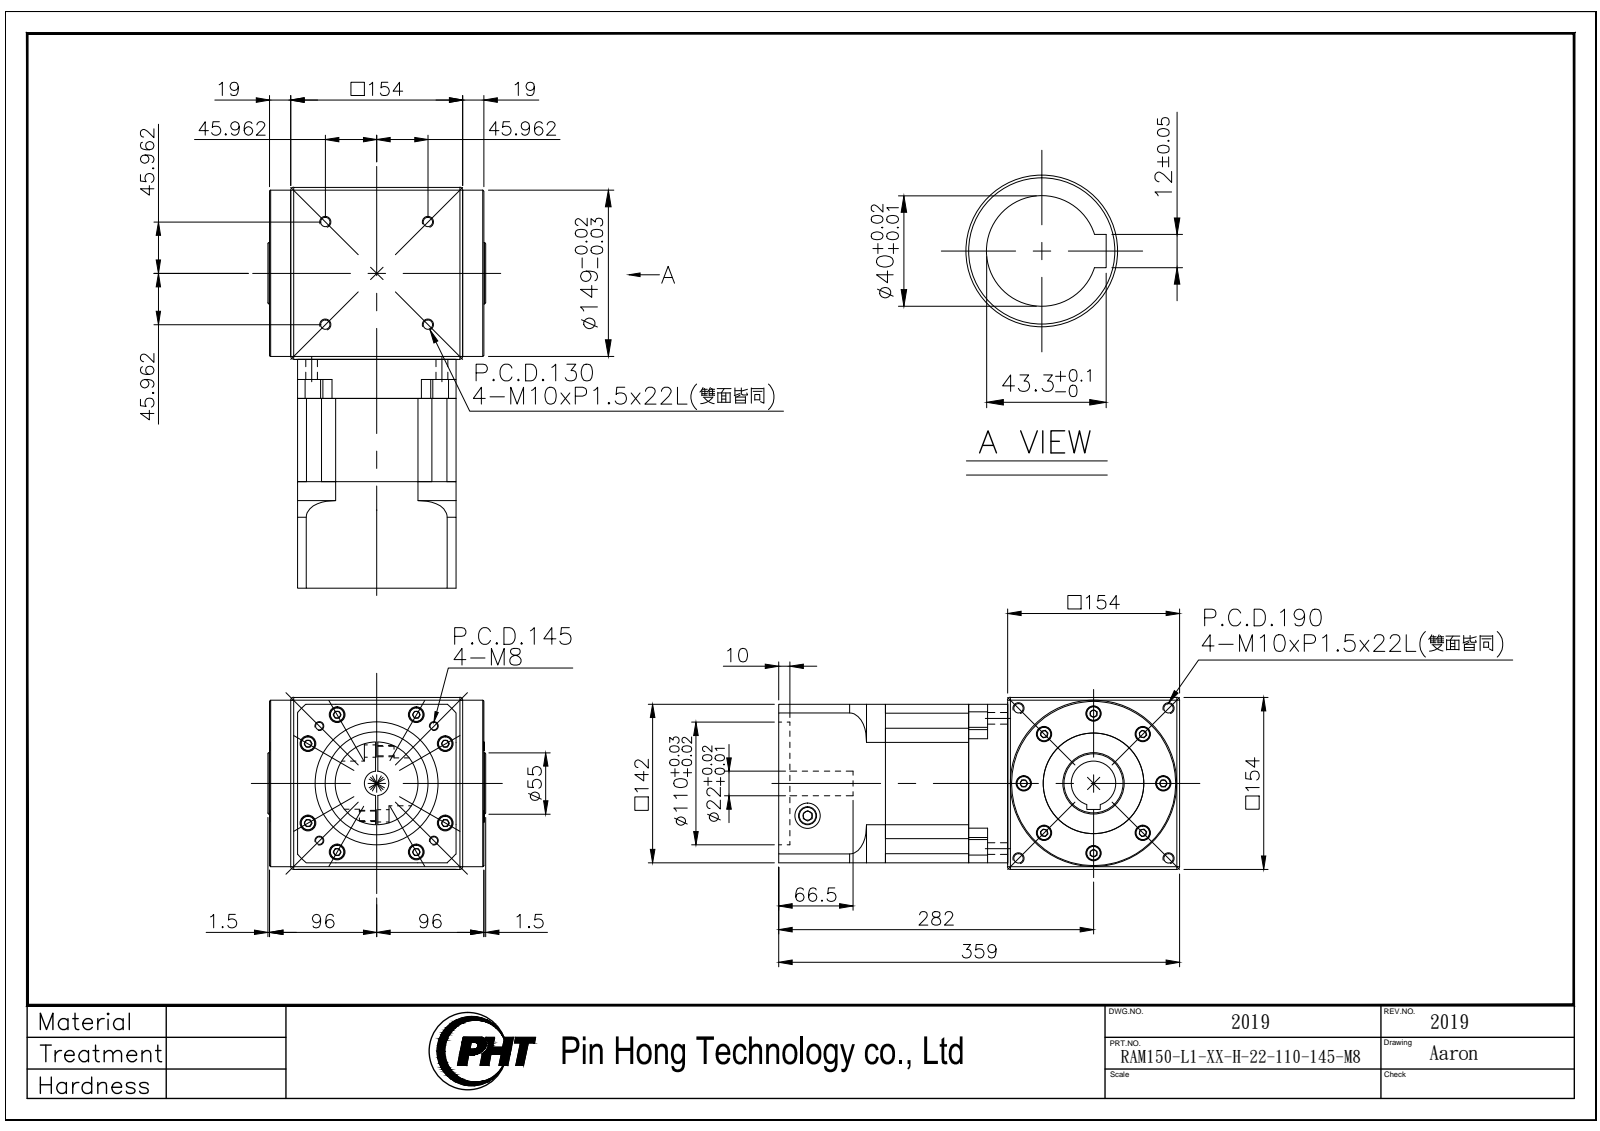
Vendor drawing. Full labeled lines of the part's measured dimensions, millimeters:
Part name (STEP PRODUCT): RAM150-L1-XX-H-22-110-145-M8_2019
STEP written by: SolidWorks 2016 (AUTOMOTIVE_DESIGN)
Units: millimetres
Bodies: 4 solids, 864 faces (428 planar, 288 cylindrical, 148 other)
Overall size (bounding box): 359 × 195 × 154
Volume: 7 568 000 mm³ · Surface area: 530 192 mm²
Round holes (diameter × count): ⌀8.5 ×12, ⌀9 ×8, ⌀11 ×8, ⌀14 ×8, ⌀17.5 ×8, ⌀6.8 ×4, ⌀10.5 ×4, ⌀22.5 ×2, ⌀22 ×1, ⌀40 ×1, ⌀40.6 ×1, ⌀92 ×1
Round bosses / shafts (diameter × count): ⌀16 ×12, ⌀13 ×8, ⌀149 ×1, ⌀130 ×1, ⌀90 ×1, ⌀74 ×1, ⌀55 ×1
Partial cylindrical surfaces — rounded edges, fillets, slot ends (radius × count): R10 ×4, R80 ×1, R95 ×1, R107.4 ×1
Main face-to-face distances: 6, 148, 154, 142, 74.5, 35, 109.5, 263.5, 189, 167
Hole centre spacings: 71, 18.72, 18.79, 23.06, 47.83, 67.34, 82.93, 87.37
